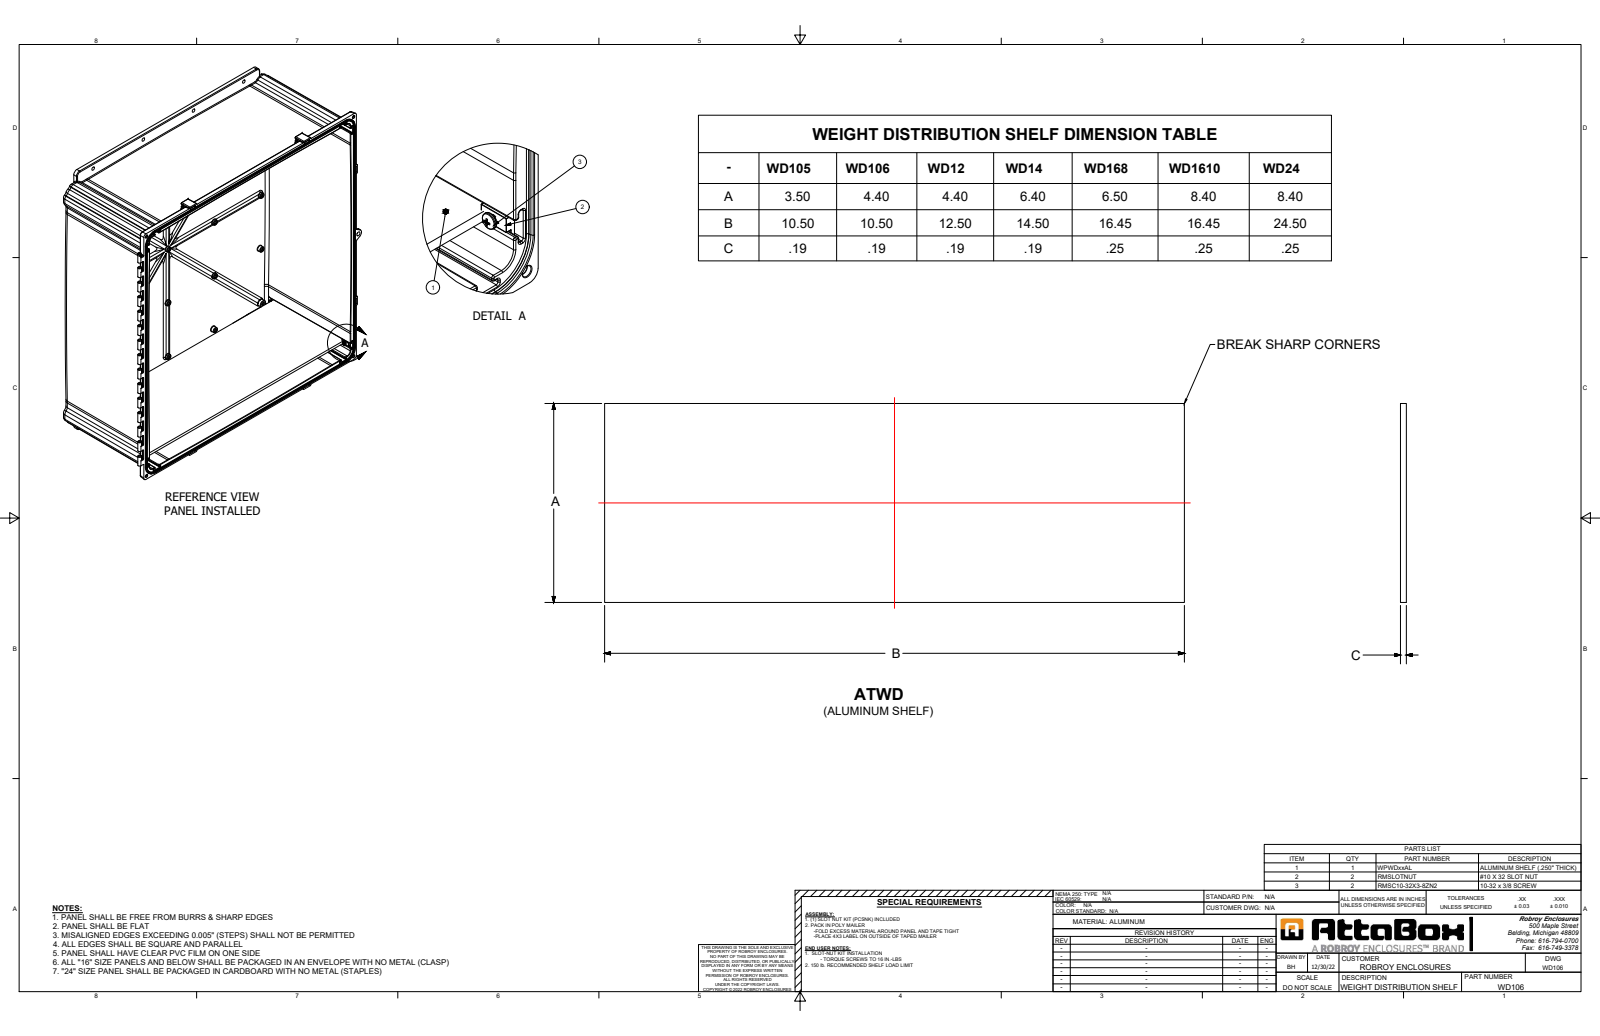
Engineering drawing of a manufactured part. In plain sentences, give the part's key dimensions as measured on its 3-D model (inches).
The part is named "WD10-6_Default". Its 3-D file was written by "SolidWorks 2023 (CONFIG_CONTROL_DESIGN)". It is 1 solid with 6 faces: 6 planar, 0 cylindrical and 0 other. Overall it measures 10.5 by 4.4 by 0.19 inches. Its volume is 8.778 cubic inches and its surface area 98.06 square inches. The main face-to-face distances are 0.19, 4.4, 10.5.
